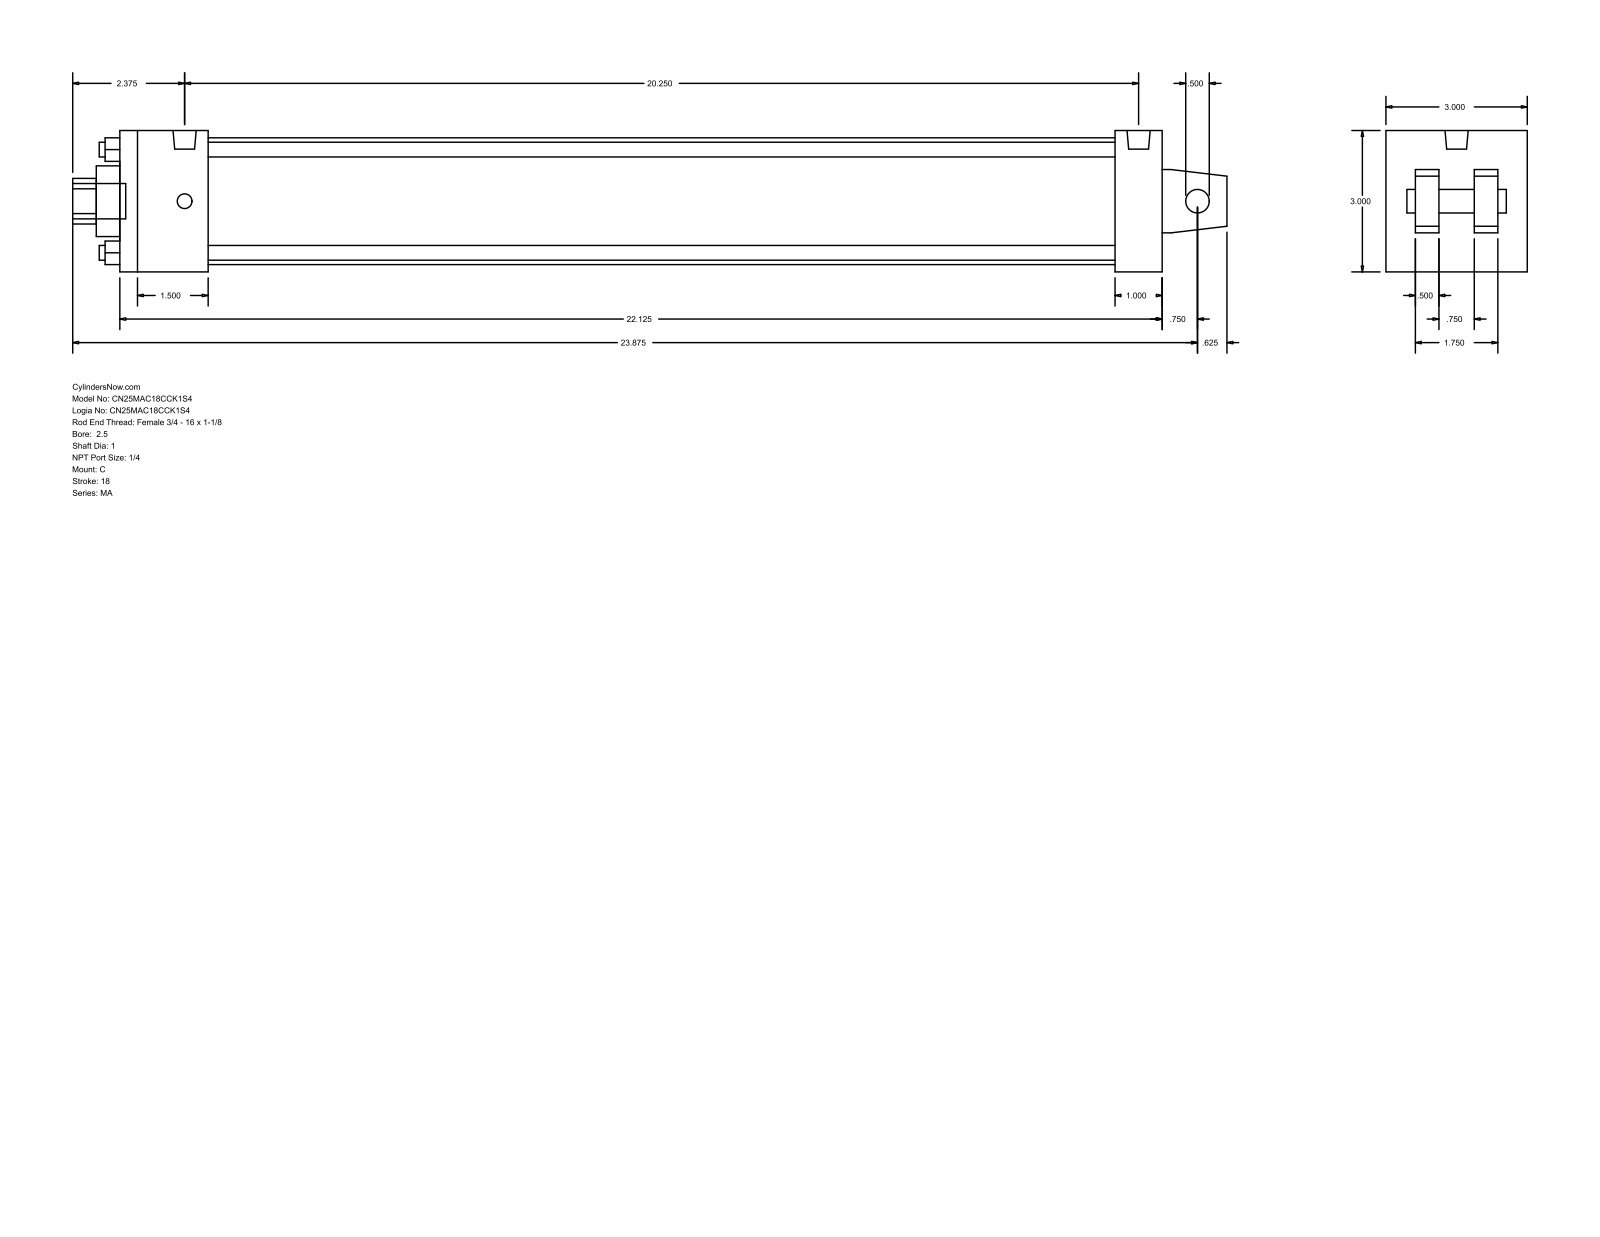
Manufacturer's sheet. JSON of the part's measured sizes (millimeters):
{"part_name": "MA_C__0250_1", "step_written_by": "GSSL Pune (CONFIG_CONTROL_DESIGN)", "units": "millimeters", "bodies": {"solids": 0, "faces": 103, "planar": 76, "cylindrical": 27, "other": 0}, "overall_size": [622.3, 76.2, 76.2], "round_holes": [[7.94, 4], [12.7, 1], [25.4, 1], [38.1, 1], [68.33, 1]], "round_bosses_or_shafts": [[7.94, 4], [12.49, 2], [19.05, 1]], "partial_cylinders_radius": [[12.29, 1]], "face_to_face_distances": [76.2, 561.98, 47.63, 12.7, 15.87, 60.33, 25.4, 28.57, 536.58, 488.95], "hole_center_spacings": [39.33, 55.62, 78.66]}
